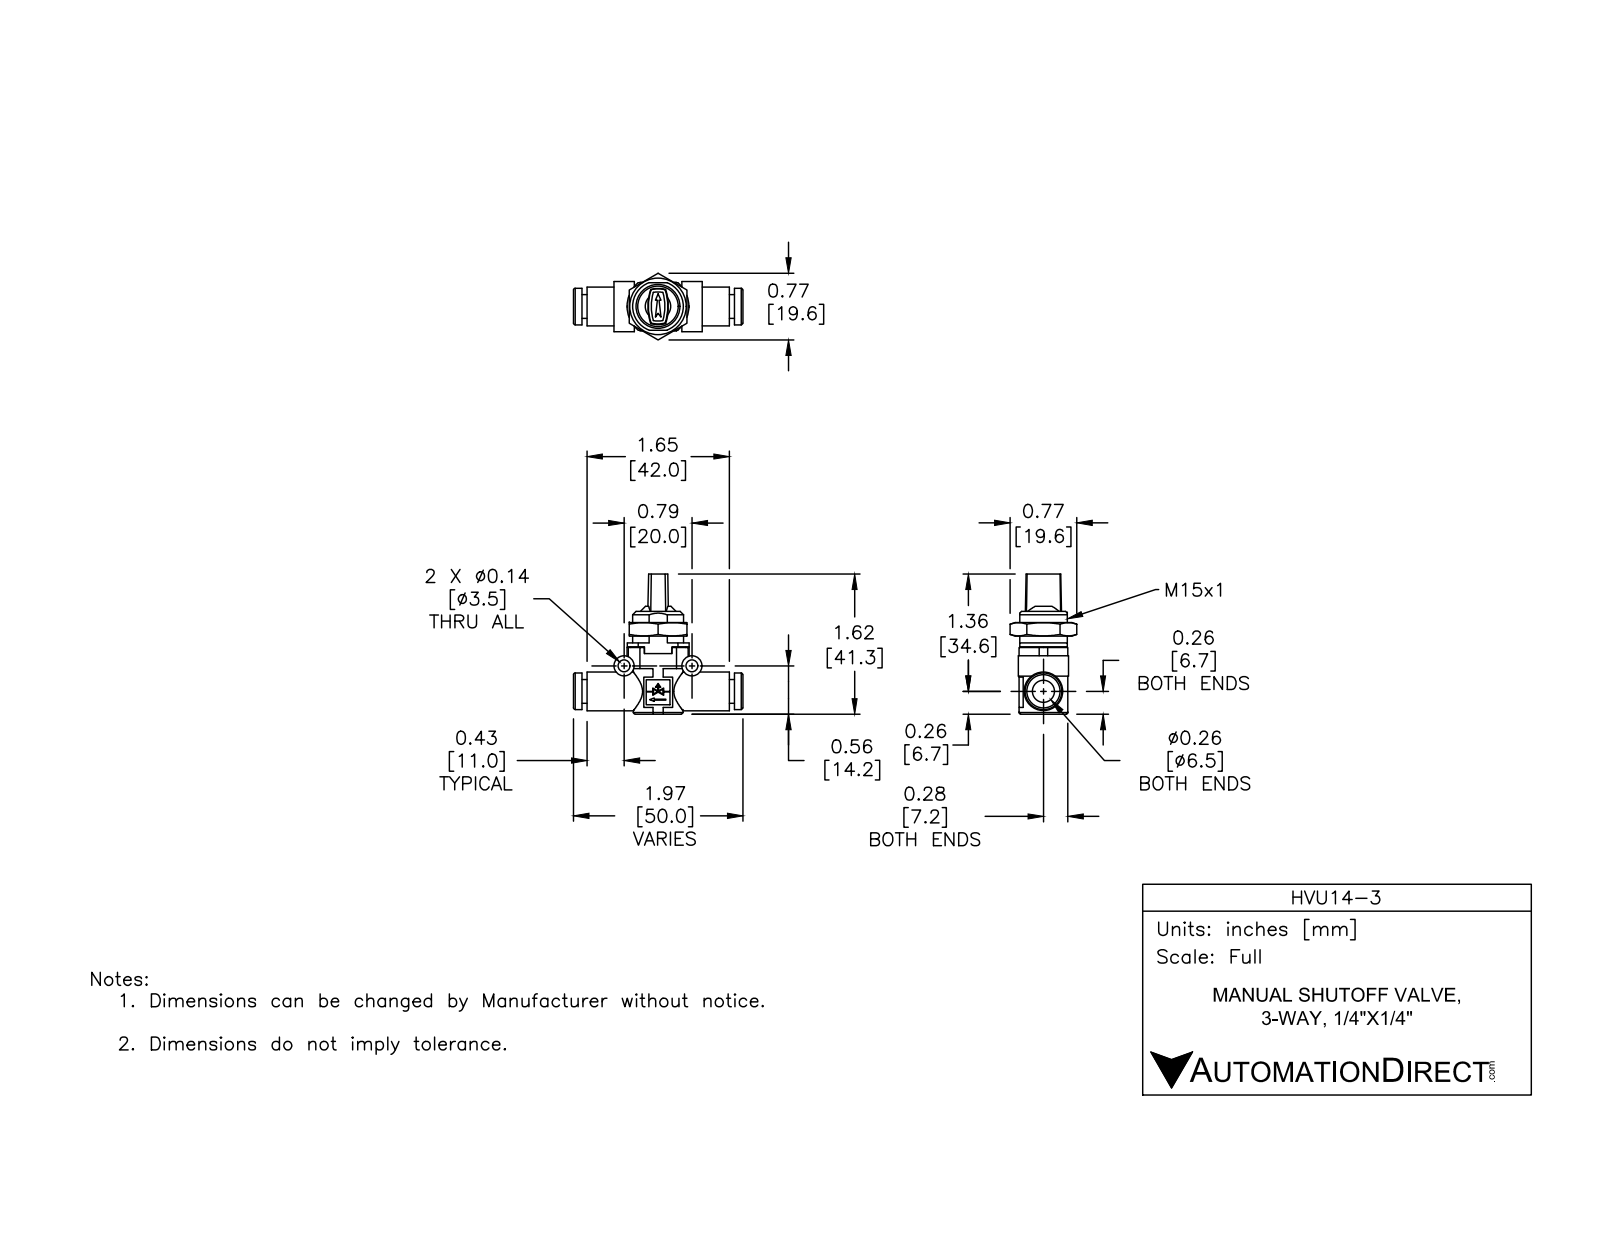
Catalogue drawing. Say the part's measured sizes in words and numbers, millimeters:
The part is named "HVU14-3". Its 3-D file was written by "SolidWorks 2015 (CONFIG_CONTROL_DESIGN)". It is 4 solids with 190 faces: 121 planar, 49 cylindrical and 20 other. Overall it measures 50 by 41.25 by 19.63 millimeters. Its volume is 8 898 cubic millimeters and its surface area 6 716 square millimeters. Round holes: 2 of diameter 3.5, 1 of diameter 6.5, 1 of diameter 7.5, 1 of diameter 12. Round bosses or shafts: 2 of diameter 6, 1 of diameter 14.65, 1 of diameter 11.4, 1 of diameter 10.8, 1 of diameter 7. Partial cylindrical surfaces (rounded edges, fillets, slot ends): 2 of radius 0.5, 2 of radius 2.5, 2 of radius 7.03, 2 of radius 14.56, 1 of radius 7.5, 1 of radius 9.12. The main face-to-face distances are 14, 17.85, 16.5, 4, 1.5, 14.17, 2, 43.5, 17, 3.15. The hole center spacings are 20.
